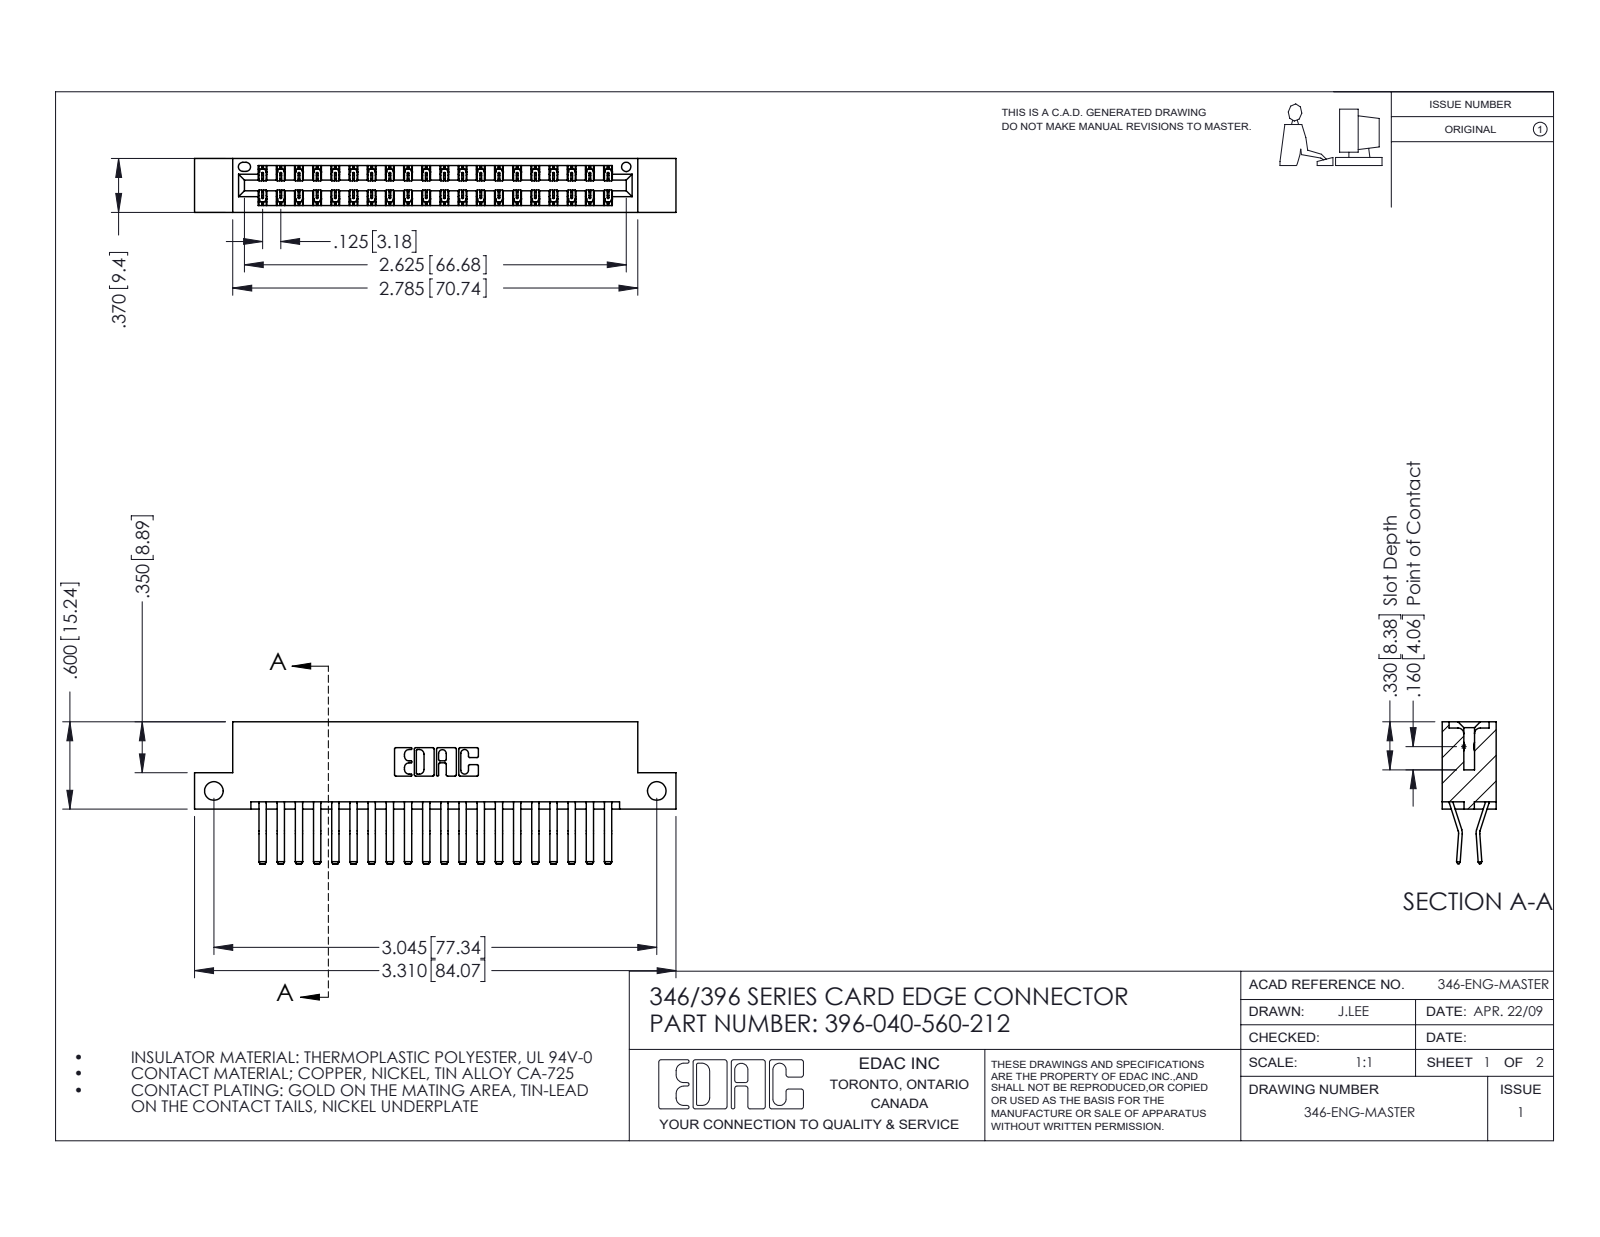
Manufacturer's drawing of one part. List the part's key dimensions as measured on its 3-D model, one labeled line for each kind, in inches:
Part name (STEP PRODUCT): 396-040-560-212; 346 Part_Flush Mounting Lugs - Side Mount; 345-292-001_560 Tail
STEP written by: SolidWorks 2016 (CONFIG_CONTROL_DESIGN)
Units: inches
Bodies: 41 solids, 2282 faces (1476 planar, 806 cylindrical, 0 other)
Overall size (bounding box): 3.31 × 0.975 × 0.37
Volume: 0.501 in³ · Surface area: 17.81 in²
Round holes (diameter × count): ⌀0.128 ×2, ⌀0.064 ×1
Partial cylindrical surfaces — rounded edges, fillets, slot ends (radius × count): R0.006 ×60, R0.01 ×22, R0.007 ×6, R0.031 ×6, R0.026 ×3, R0.01 ×2, R0.014 ×2, R0.022 ×2
Main face-to-face distances: 0.048, 0.322, 0.25, 0.37, 0.025, 0.072, 0.298, 0.275, 0.148, 0.222
Hole centre spacings: 3.045
